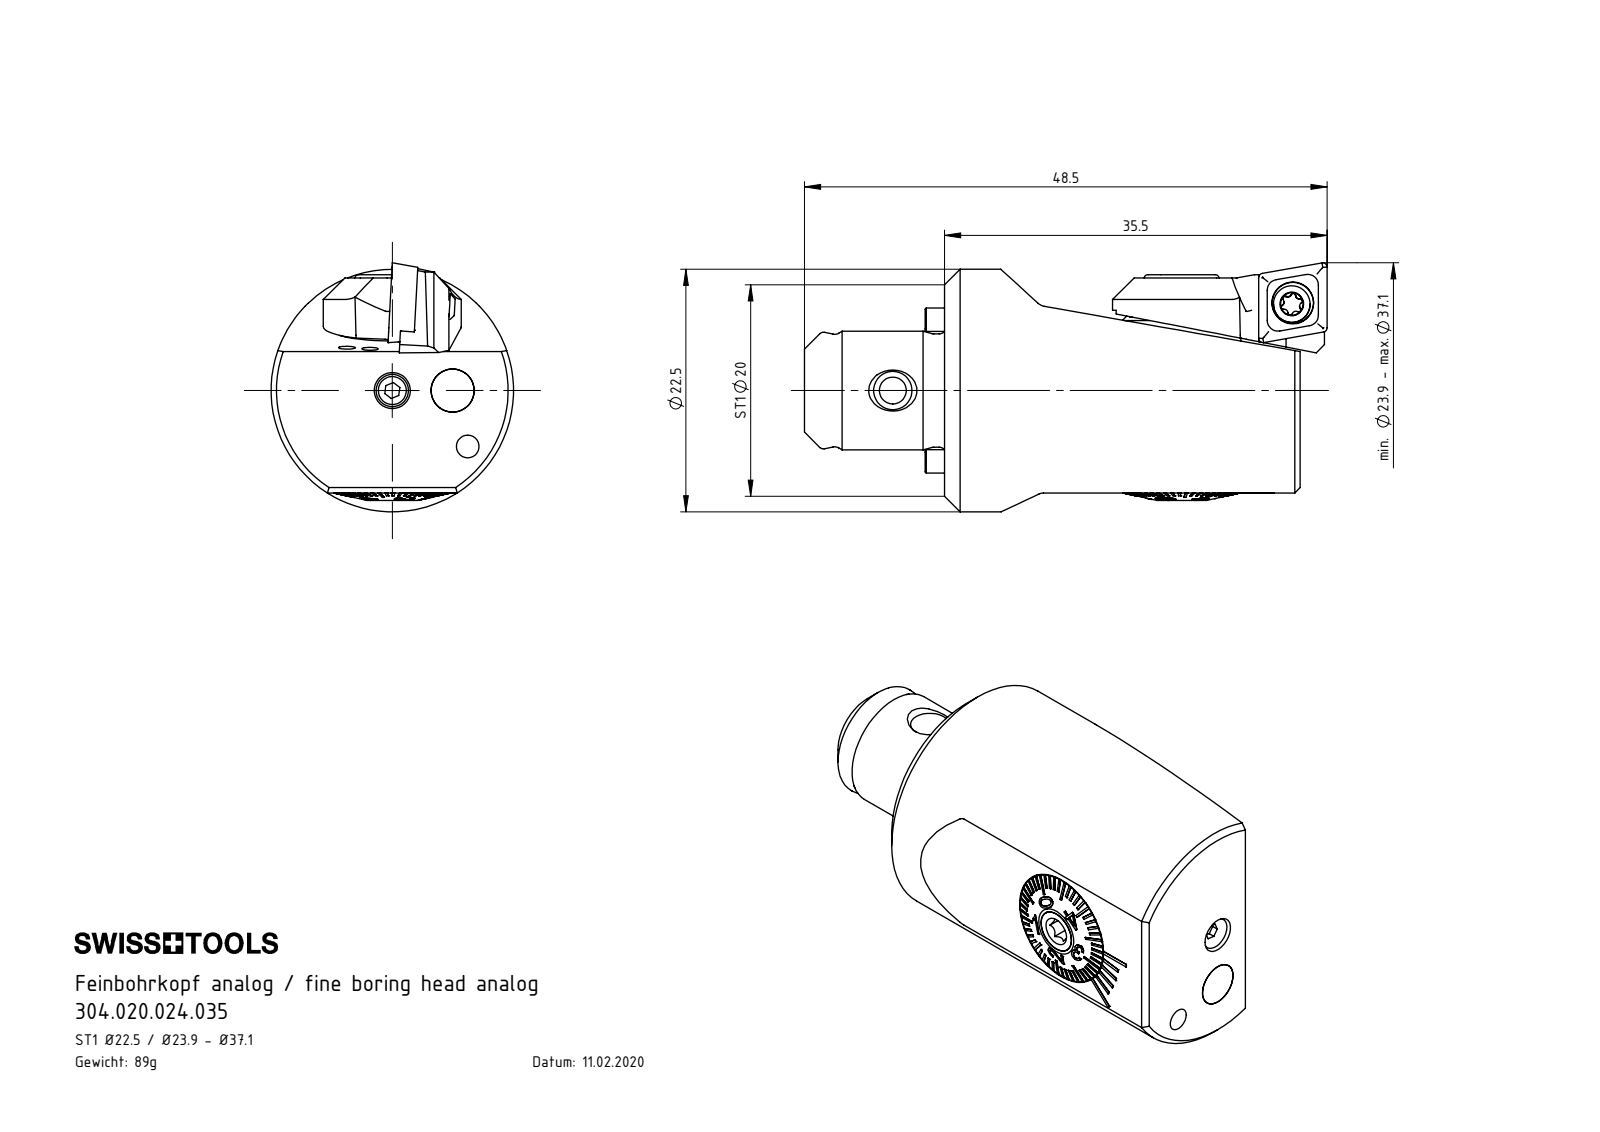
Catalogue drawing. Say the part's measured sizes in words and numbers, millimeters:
The part is named "F20-BG1.008.006_B; F20-BG3.004.018_A; Klebstoff D4; DIN 7984 - M4 x 6_PreviewCfg (+8 more)". Its 3-D file was written by "SolidWorks 2017 (AUTOMOTIVE_DESIGN)". It is 15 solids with 544 faces: 294 planar, 70 cylindrical and 180 other. Overall it measures 46 by 22.5 by 22.5 millimeters. Its volume is 11 492 cubic millimeters and its surface area 7 410 square millimeters. Round holes: 4 of diameter 2.1, 2 of diameter 1.5, 2 of diameter 1.8, 2 of diameter 3, 2 of diameter 3.3, 1 of diameter 1.08, 1 of diameter 1.9, 1 of diameter 2.5, 1 of diameter 4, 1 of diameter 4.2, 1 of diameter 4.5, 1 of diameter 5.4. Round bosses or shafts: 2 of diameter 11, 2 of diameter 4, 2 of diameter 3.95, 1 of diameter 22.5, 1 of diameter 10.98, 1 of diameter 10.85, 1 of diameter 10.8, 1 of diameter 10.5. Partial cylindrical surfaces (rounded edges, fillets, slot ends): 6 of radius 0.3, 2 of radius 1.25, 2 of radius 1.48, 2 of radius 2, 2 of radius 5.55, 1 of radius 1.05. The main face-to-face distances are 33, 3.7, 1.5, 0.8, 2.9, 2.8, 1.4, 12.6, 15.5, 16.3. The hole center spacings are 6.65, 8.69, 5.38, 5.6, 7.15, 8.71, 13.3, 13.75.
